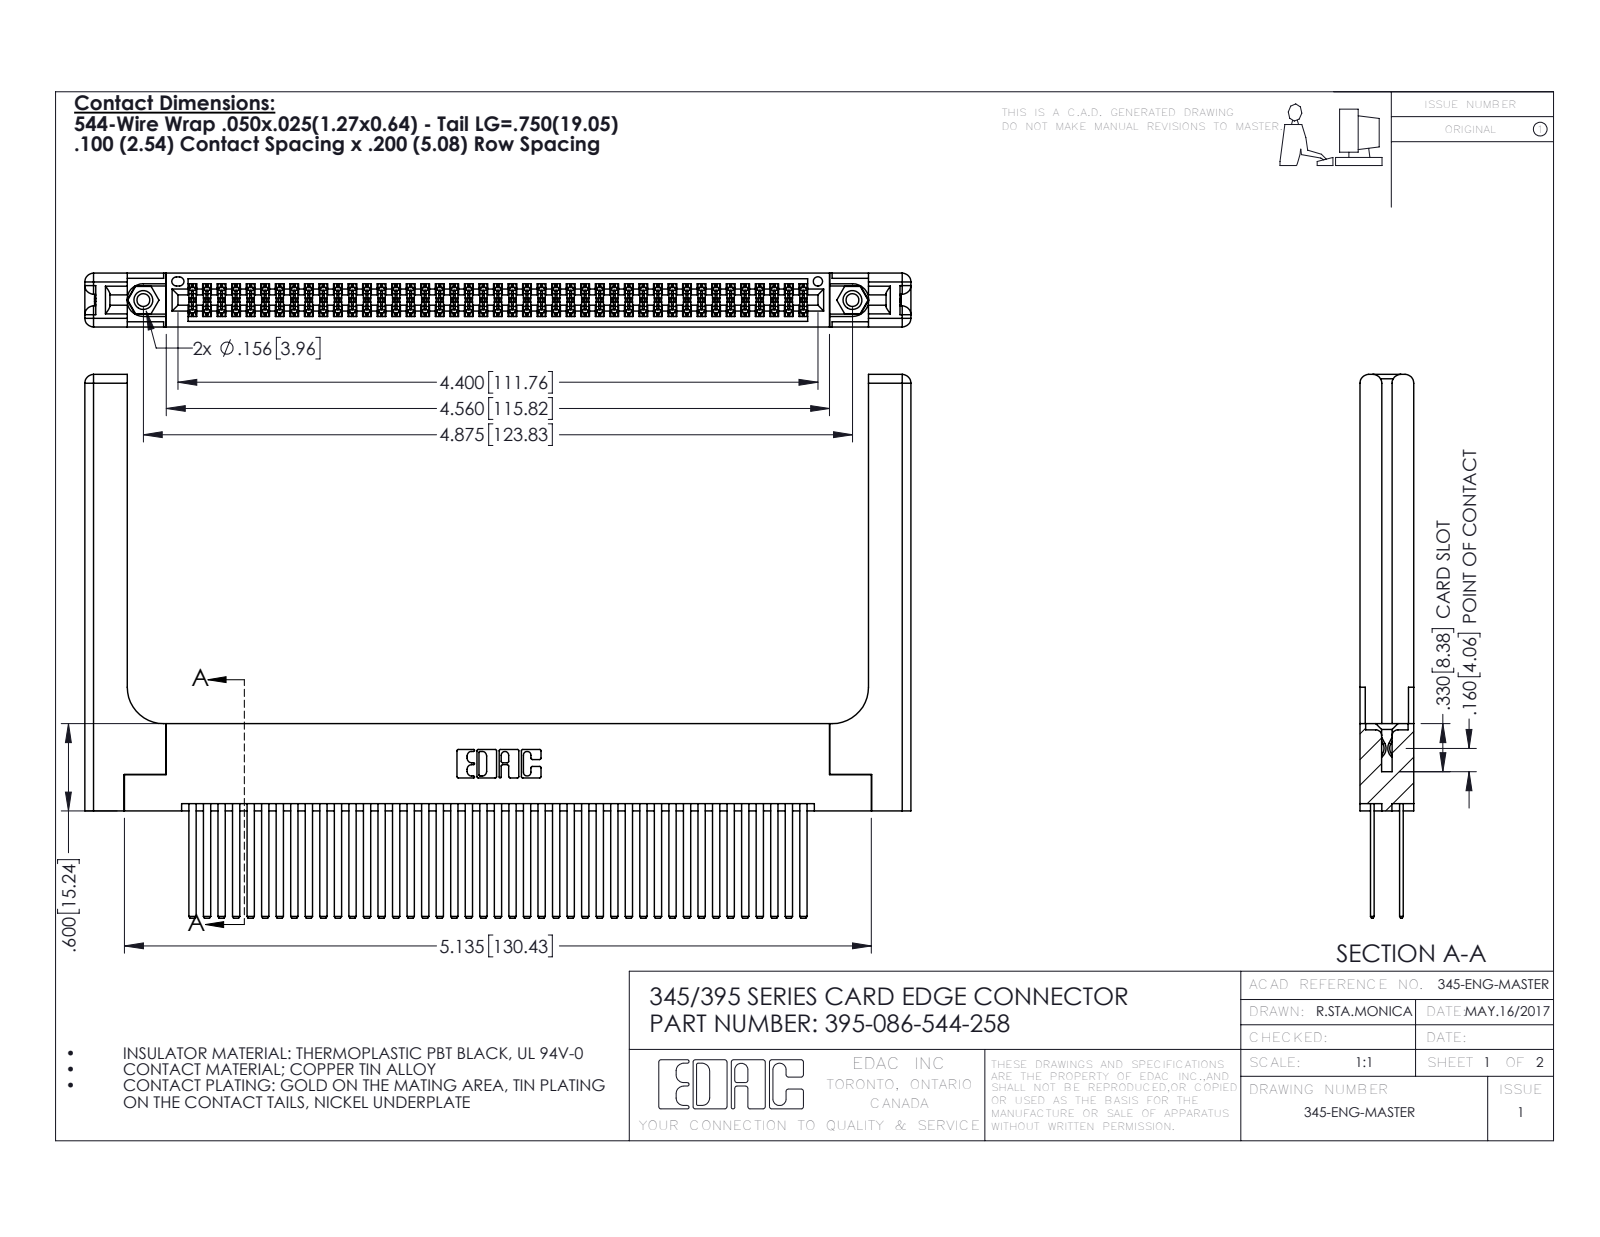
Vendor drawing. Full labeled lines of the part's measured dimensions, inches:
Part name (STEP PRODUCT): 345-292-001_345-293-144; 345-220-058_345-220-058; 395-086-544-258; 345 Part_Flush Mounting Lugs - 0.156 Dia-TH (+1 more)
STEP written by: SolidWorks 2016 (CONFIG_CONTROL_DESIGN)
Units: inches
Bodies: 91 solids, 4166 faces (2722 planar, 1384 cylindrical, 60 other)
Overall size (bounding box): 5.679 × 3.737 × 0.37
Volume: 1.446 in³ · Surface area: 48.24 in²
Round holes (diameter × count): ⌀0.089 ×2, ⌀0.125 ×2, ⌀0.156 ×2, ⌀0.064 ×1
Round bosses / shafts (diameter × count): ⌀0.155 ×2
Partial cylindrical surfaces — rounded edges, fillets, slot ends (radius × count): R0.006 ×129, R0.01 ×22, R0.06 ×16, R0.007 ×6, R0.031 ×6, R0.026 ×3, R0.014 ×2, R0.019 ×2
Main face-to-face distances: 0.072, 0.298, 0.2, 0.098, 0.272, 0.025, 0.37, 0.225, 0.175, 0.148
Hole centre spacings: 0.27, 4.639, 4.875
